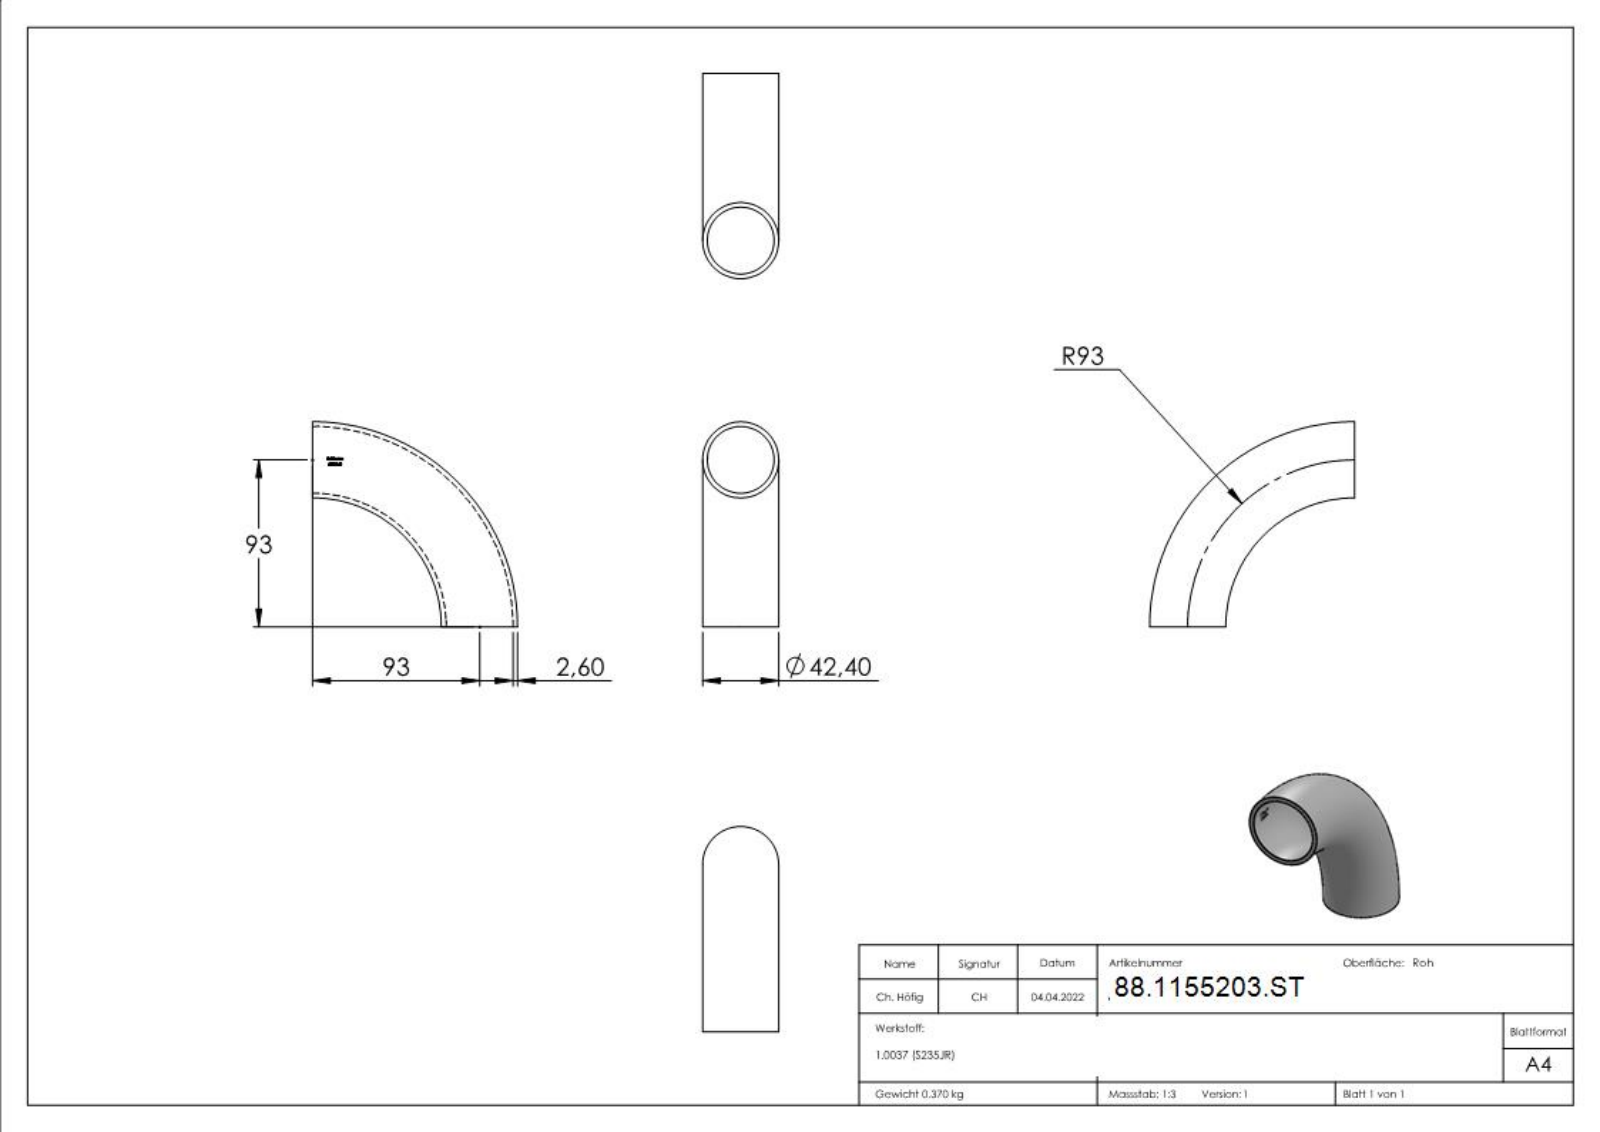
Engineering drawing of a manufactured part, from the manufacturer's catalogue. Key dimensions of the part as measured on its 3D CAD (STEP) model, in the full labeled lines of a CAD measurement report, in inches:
Part name (STEP PRODUCT): 55203-ST
STEP written by: SolidWorks 2018 (CONFIG_CONTROL_DESIGN)
Units: inches
Bodies: 1 solid, 221 faces (91 planar, 0 cylindrical, 130 other)
Overall size (bounding box): 4.496 × 4.496 × 1.669
Volume: 2.898 in³ · Surface area: 57.64 in²
Main face-to-face distances: 0.117, 0.015, 0.044, 0.052, 0.08, 0.144, 0.129, 0.296, 0.221, 0.161
